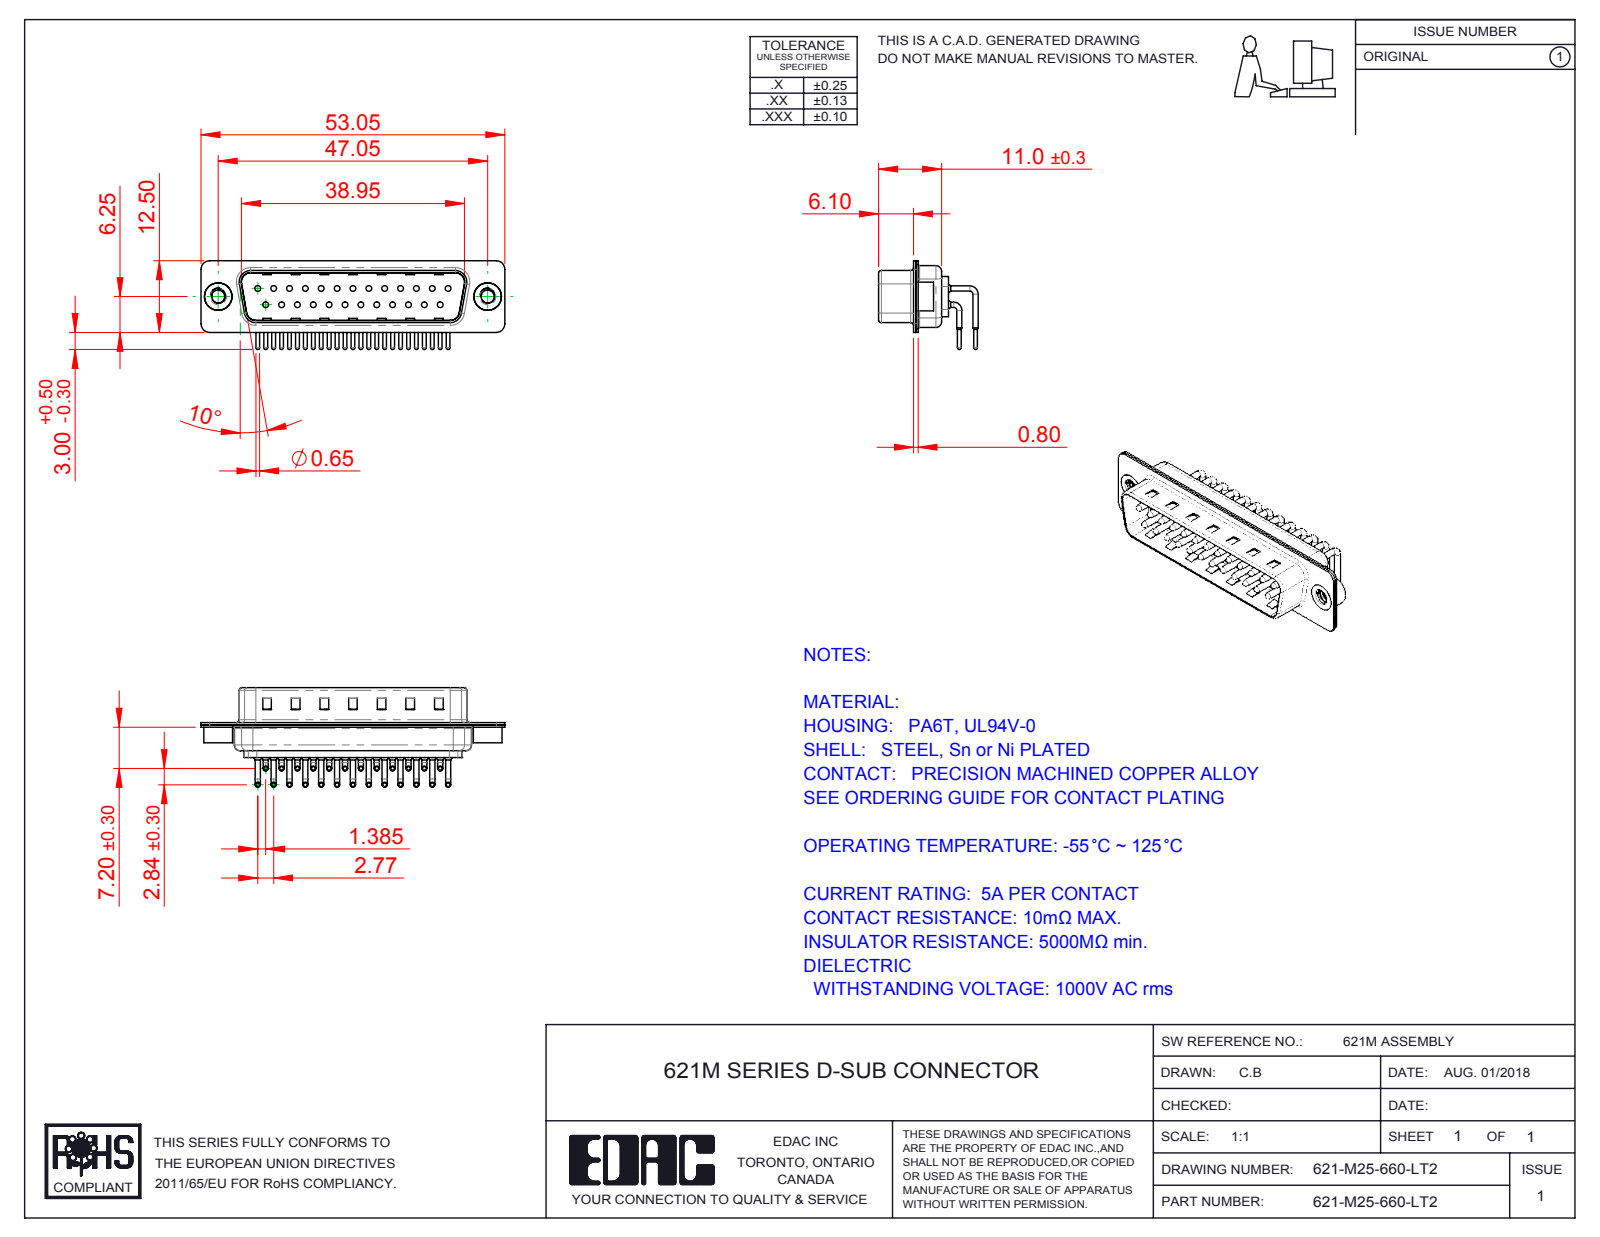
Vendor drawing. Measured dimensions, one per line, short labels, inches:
name: 621M Shell Rear_25 Contacts; 621M Shell Front_25 Contacts; 621M Contact Row 1; 621M Contact Row 2 (+3 more)
written by: SolidWorks 2016 (CONFIG_CONTROL_DESIGN)
unit: in
bodies: 30 solids, 3126 faces (1771 planar, 1037 cylindrical, 318 other)
size: 2.089 × 0.685 × 0.61
volume: 0.175 in³; area: 11.76 in²
holes: 25× ⌀0.039, 25× ⌀0.067, 25× ⌀0.079, 2× ⌀0.089, 2× ⌀0.157, 2× ⌀0.189
bosses: 50× ⌀0.035, 25× ⌀0.059, 25× ⌀0.026, 2× ⌀0.197, 2× ⌀0.193
rounds: 25× R0.04, 16× R0.059, 12× R0.079, 8× R0.02, 8× R0.063, 4× R0.01, 4× R0.024, 4× R0.026
face distances: 0.016, 0.033, 0.376, 0.343, 0.049, 0.409, 0.059, 0.075, 0.014, 0.24
hole spacings: 0.124, 0.327, 0.109, 0.218, 0.436, 0.654, 0.198, 0.198
